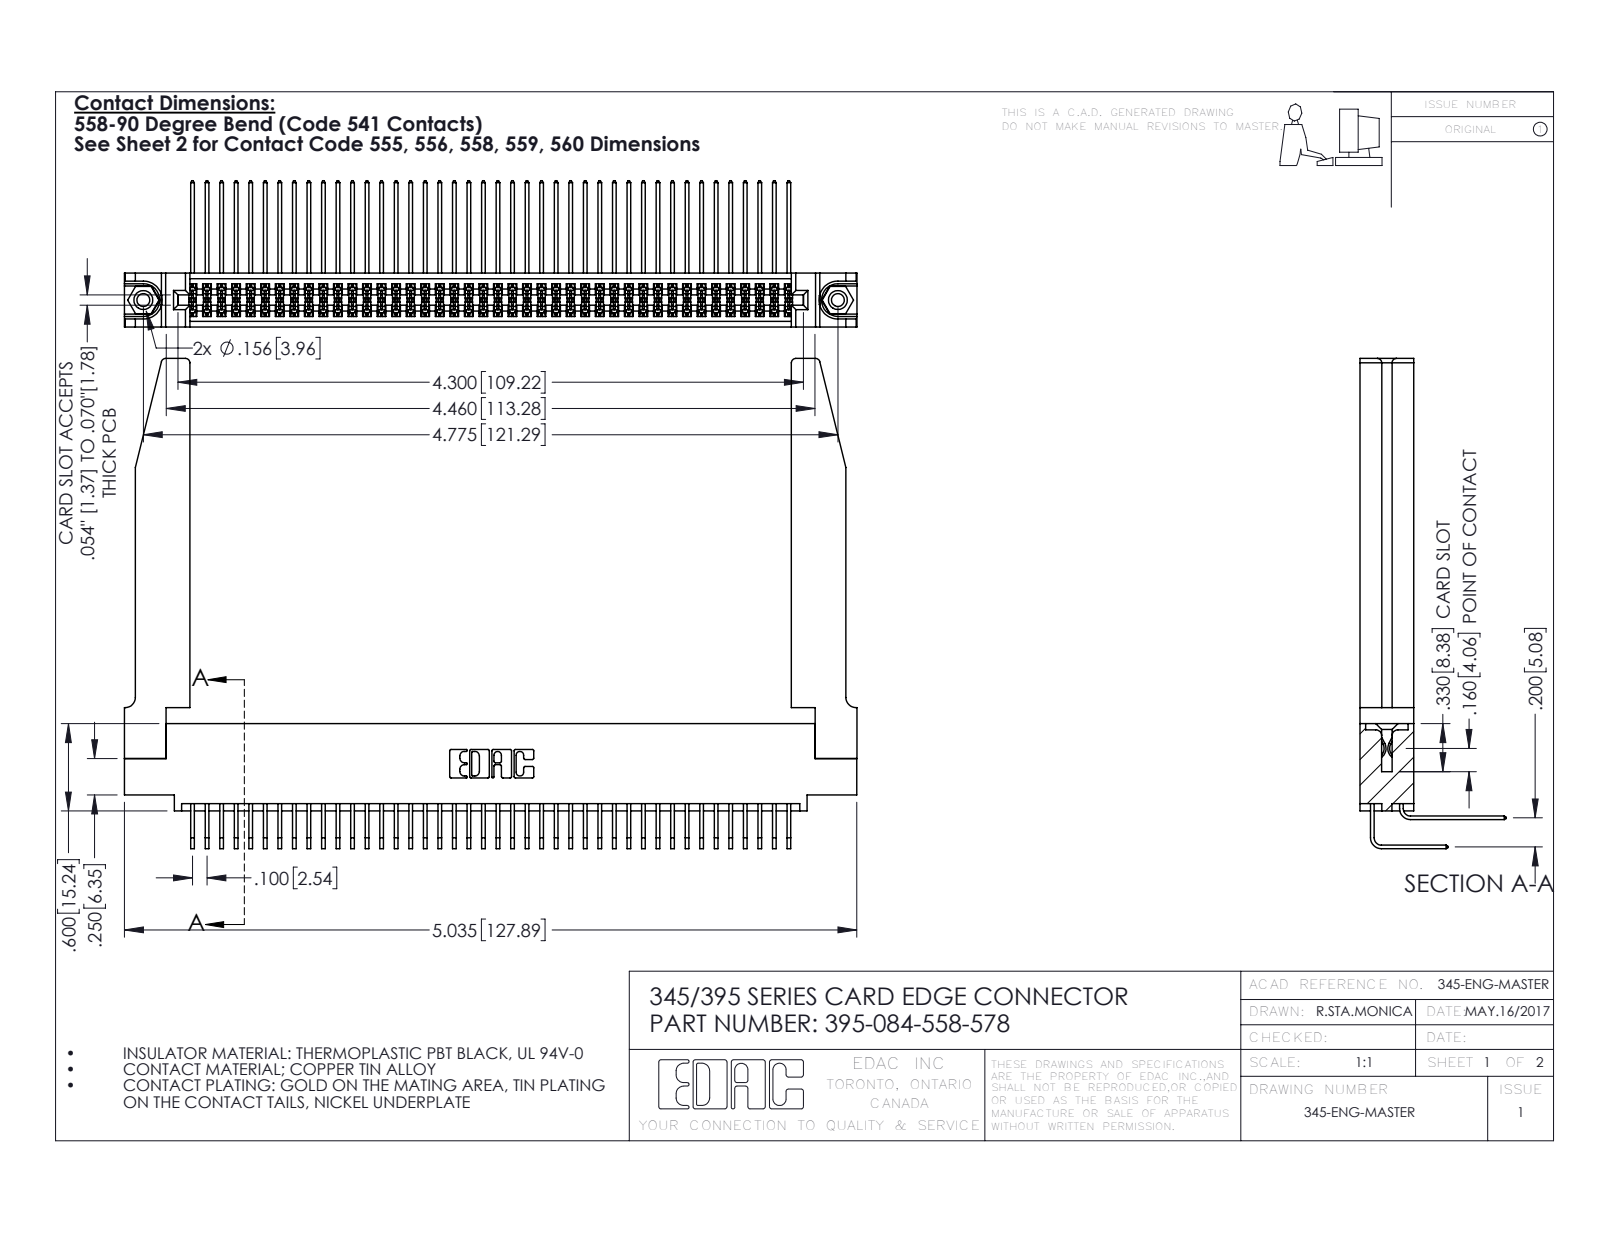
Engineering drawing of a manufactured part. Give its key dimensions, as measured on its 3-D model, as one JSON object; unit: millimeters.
{"part_name": "345-292-001_558 559 Tail - 1; 345-250-001_345-250-001-102; 345 Part_0.110 Offset - 0.156 Dia-TH; 395-084-558-578 (+2 more)", "step_written_by": "SolidWorks 2016 (CONFIG_CONTROL_DESIGN)", "units": "millimeters", "bodies": {"solids": 89, "faces": 4732, "planar": 3166, "cylindrical": 1514, "other": 52}, "overall_size": [127.9, 85.6, 25.5], "volume_mm3": 20610, "surface_area_mm2": 28190, "round_holes": [[2.3, 2], [3.2, 2], [4, 2], [1.6, 1]], "round_bosses_or_shafts": [[3.9, 2]], "partial_cylinders_radius": [[0.2, 127], [0.3, 22], [0.8, 8], [0.2, 6], [0.8, 6], [0.7, 3], [0.4, 2], [0.5, 2]], "face_to_face_distances": [1.8, 9.4, 7.6, 5.1, 2.5, 6.9, 0.6, 5.7, 3.8, 3.8], "hole_center_spacings": [6.9, 115.3, 121.3]}
